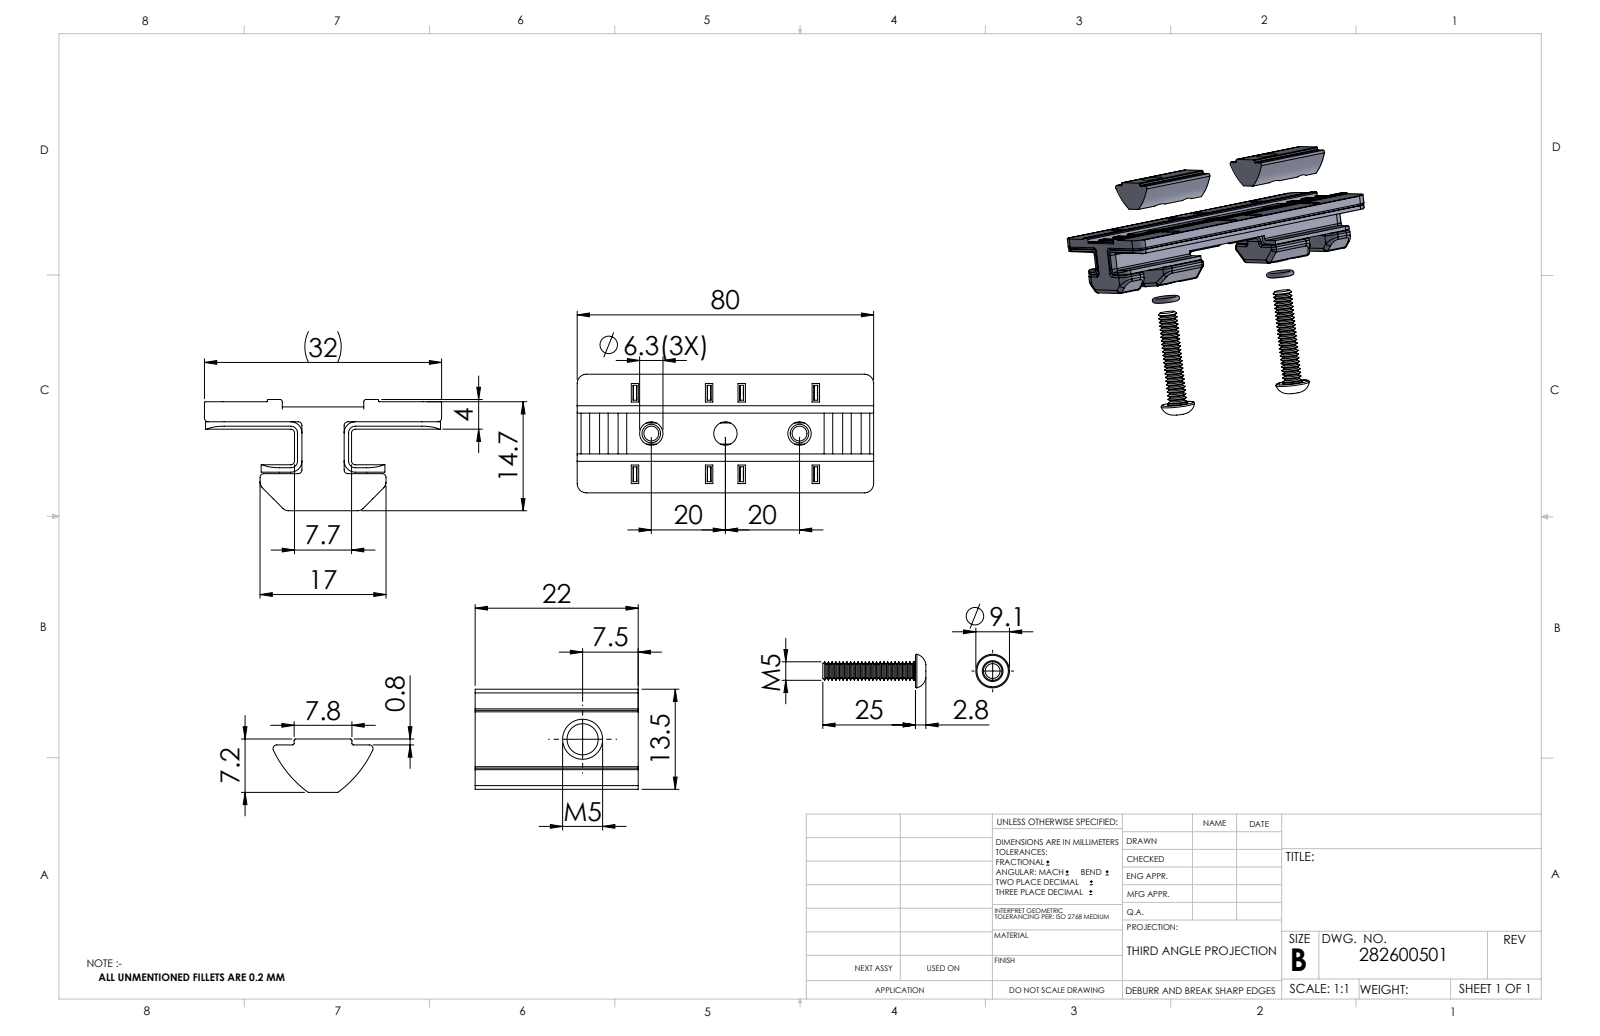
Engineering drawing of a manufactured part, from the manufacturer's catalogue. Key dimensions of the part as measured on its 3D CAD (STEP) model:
Part name (STEP PRODUCT): 282600501_c_1
STEP written by: SolidWorks 2014 (CONFIG_CONTROL_DESIGN)
Units: millimetres
Bodies: 5 solids, 553 faces (217 planar, 224 cylindrical, 112 other)
Overall size (bounding box): 80 × 32 × 15
Volume: 14 057 mm³ · Surface area: 16 378 mm²
Round holes (diameter × count): ⌀6.3 ×3
Partial cylindrical surfaces — rounded edges, fillets, slot ends (radius × count): R0.5 ×48, R1 ×38, R0.3 ×28, R2.5 ×24, R0.1 ×6, R1.5 ×4, R2 ×4, R5.3 ×2
Main face-to-face distances: 1, 2.7, 3.7, 3, 5.8, 8.8, 2, 5.7, 0.7, 7
Hole centre spacings: 20, 40
